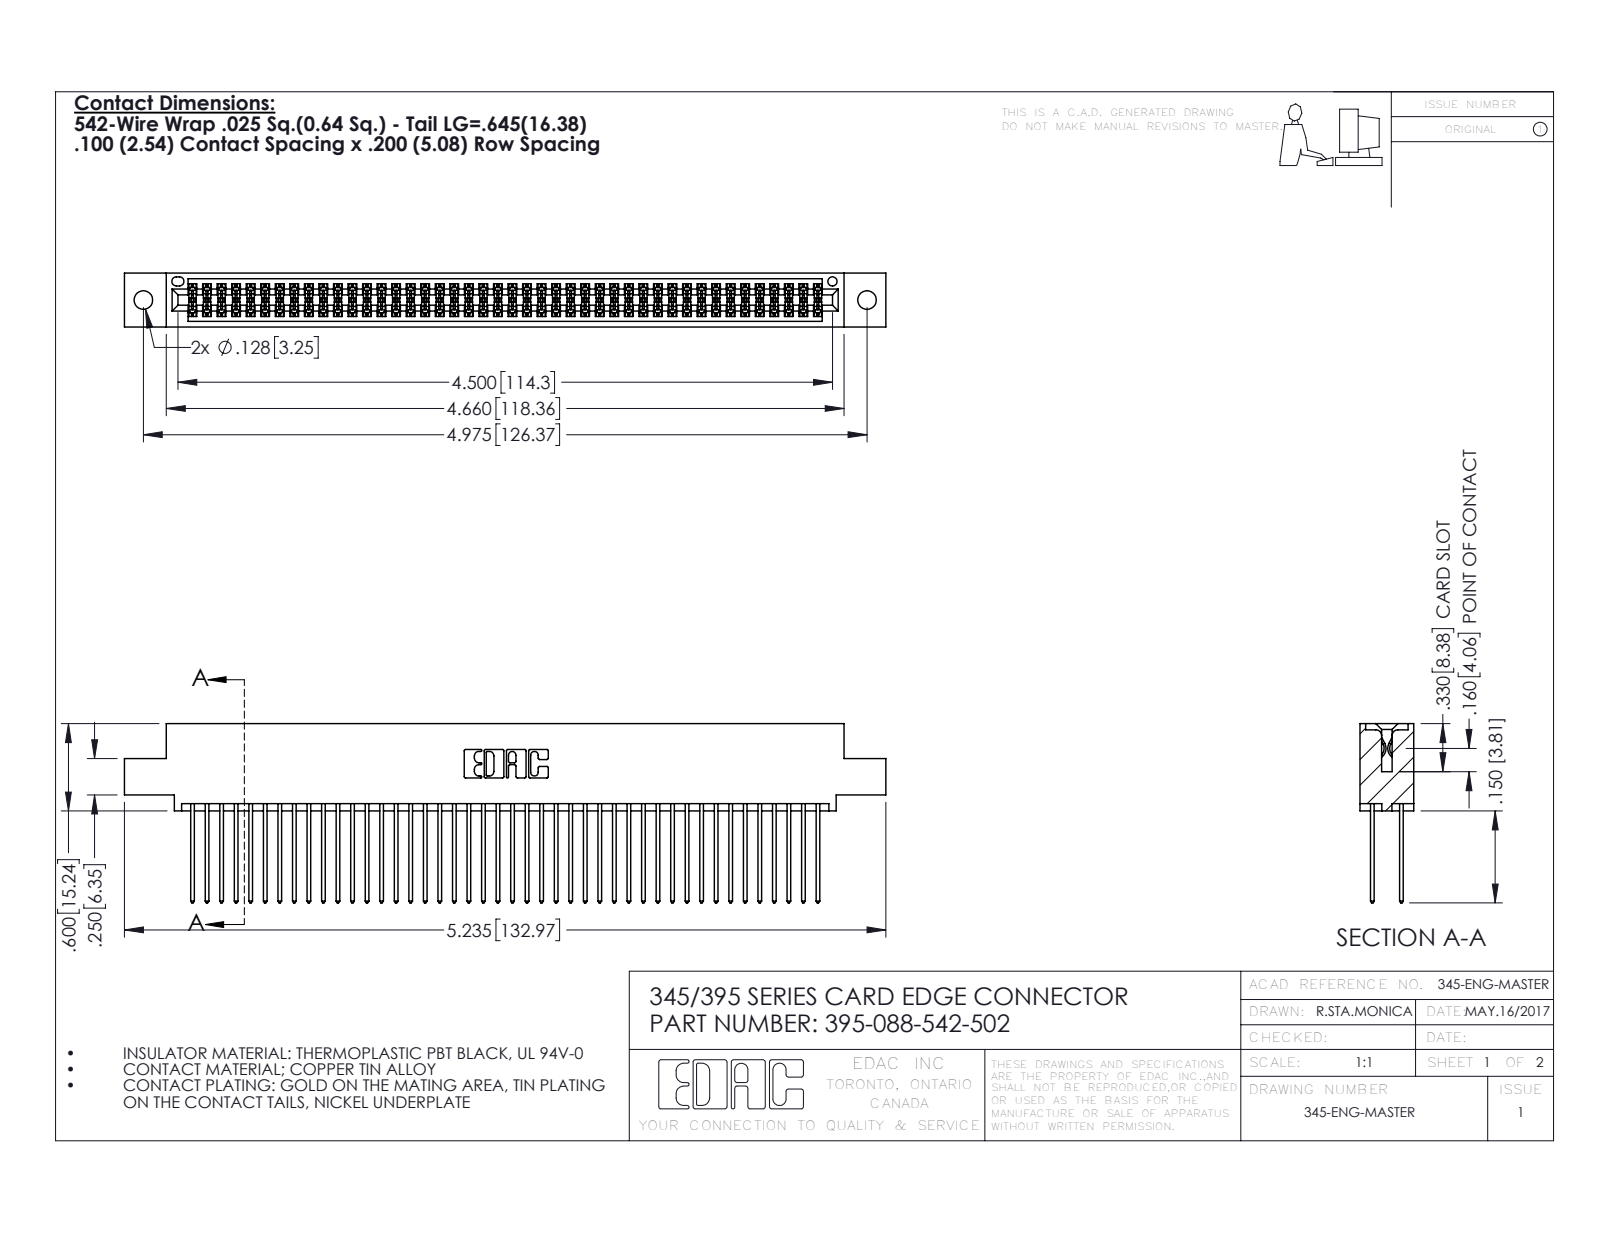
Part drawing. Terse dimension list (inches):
name: 345 Part_0.110 Offset - 0.128 Dia; 395-088-542-502; 345-292-001_345-293-142
written by: SolidWorks 2016 (CONFIG_CONTROL_DESIGN)
unit: in
bodies: 89 solids, 4530 faces (2988 planar, 1542 cylindrical, 0 other)
size: 5.235 × 1.232 × 0.37
volume: 0.808 in³; area: 33.08 in²
holes: 2× ⌀0.128, 1× ⌀0.064
rounds: 132× R0.006, 88× R0.01, 22× R0.01, 6× R0.007, 6× R0.031, 3× R0.026, 2× R0.014, 2× R0.019
face distances: 0.298, 0.072, 0.2, 0.098, 0.272, 0.025, 0.225, 0.37, 0.175, 0.149
hole spacings: 0.27, 4.739, 4.975
